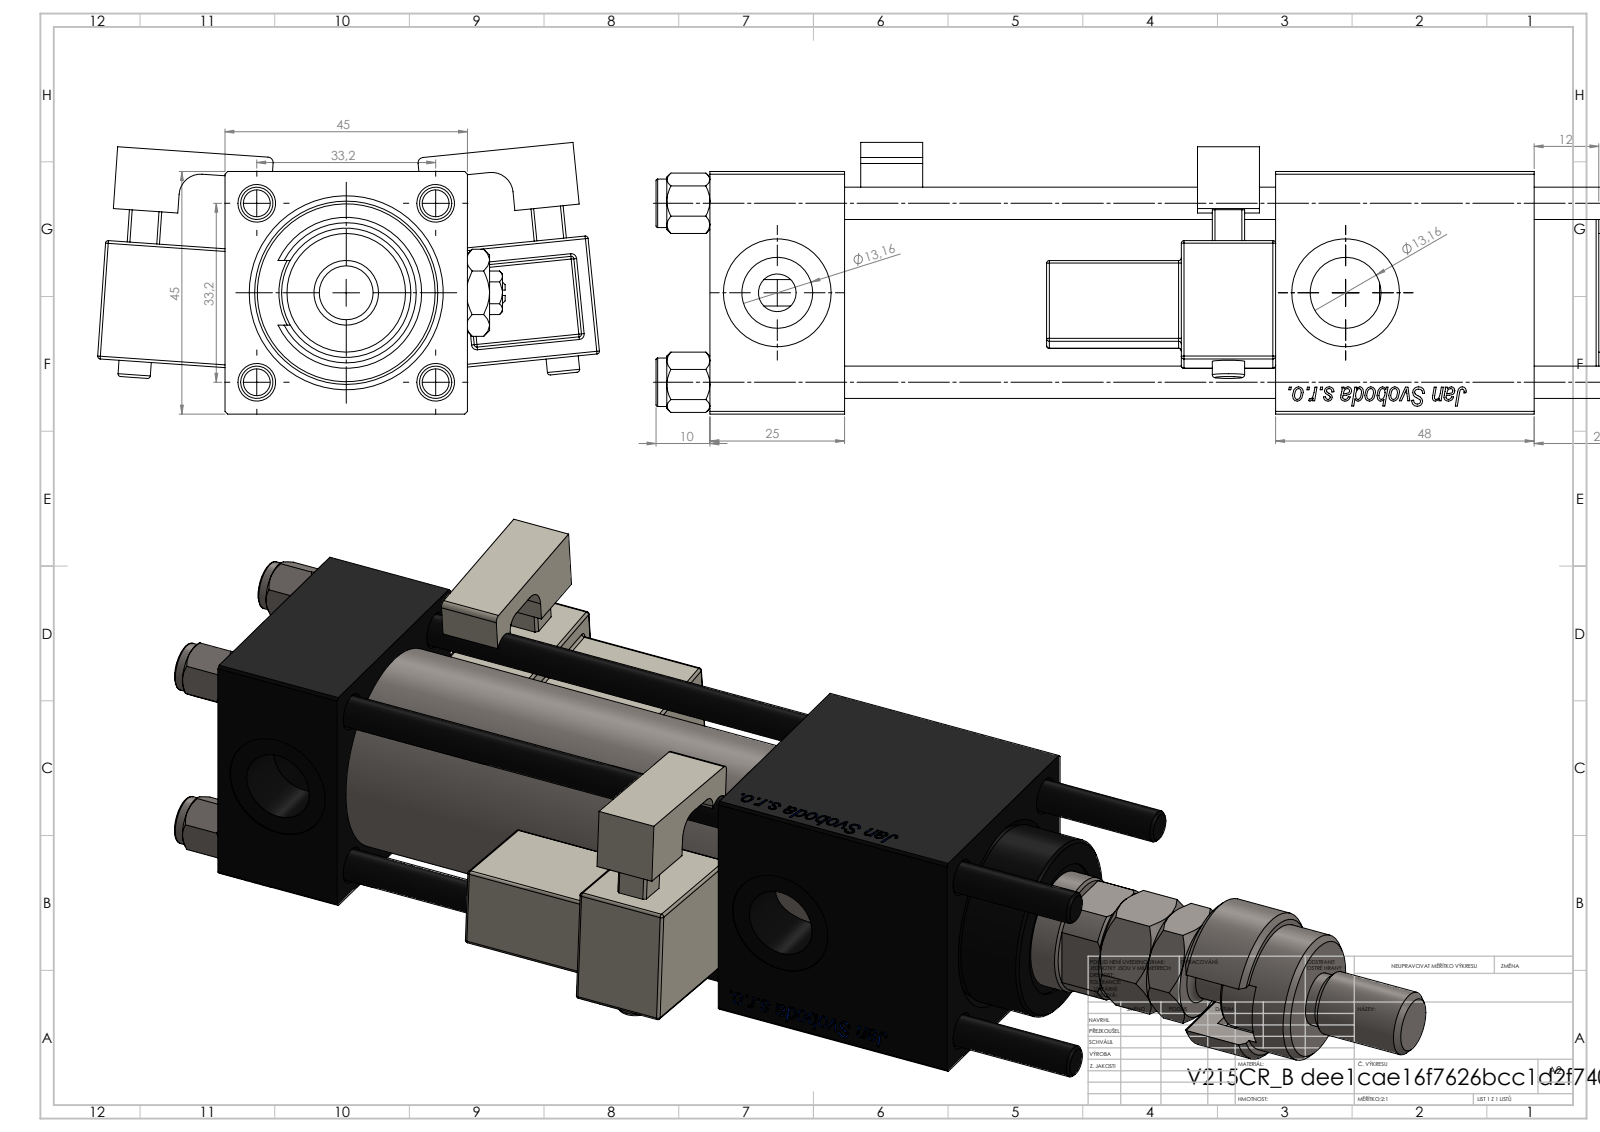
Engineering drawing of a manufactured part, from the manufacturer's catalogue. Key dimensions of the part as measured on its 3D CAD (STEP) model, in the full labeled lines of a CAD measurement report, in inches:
Part name (STEP PRODUCT): FEMALE_PART_FOR_DFA; V215CR_B-1; V215CR_B_TYCINKA; MFA (+5 more)
STEP written by: SolidWorks 2019 (CONFIG_CONTROL_DESIGN)
Units: inches
Bodies: 17 solids, 1499 faces (568 planar, 161 cylindrical, 770 other)
Overall size (bounding box): 9.803 × 3.667 × 1.984
Volume: 18.06 in³ · Surface area: 168.5 in²
Round holes (diameter × count): ⌀0.236 ×4, ⌀0.276 ×2, ⌀0.518 ×2, ⌀0.787 ×2, ⌀0.413 ×1, ⌀0.866 ×1, ⌀0.945 ×1, ⌀0.984 ×1, ⌀1.26 ×1, ⌀1.299 ×1
Round bosses / shafts (diameter × count): ⌀0.354 ×4, ⌀0.236 ×2, ⌀1.496 ×1, ⌀1.339 ×1, ⌀1.102 ×1, ⌀0.709 ×1, ⌀0.472 ×1, ⌀0.433 ×1
Partial cylindrical surfaces — rounded edges, fillets, slot ends (radius × count): R0.02 ×48, R0.039 ×2, R0.098 ×2, R0.157 ×2, R0.384 ×1, R0.413 ×1
Main face-to-face distances: 1.772, 0.984, 4.134, 3.15, 0.118, 6.024, 2.461, 1.89, 0.571, 0.787
Hole centre spacings: 0.924, 1.307, 1.848, 4.154
